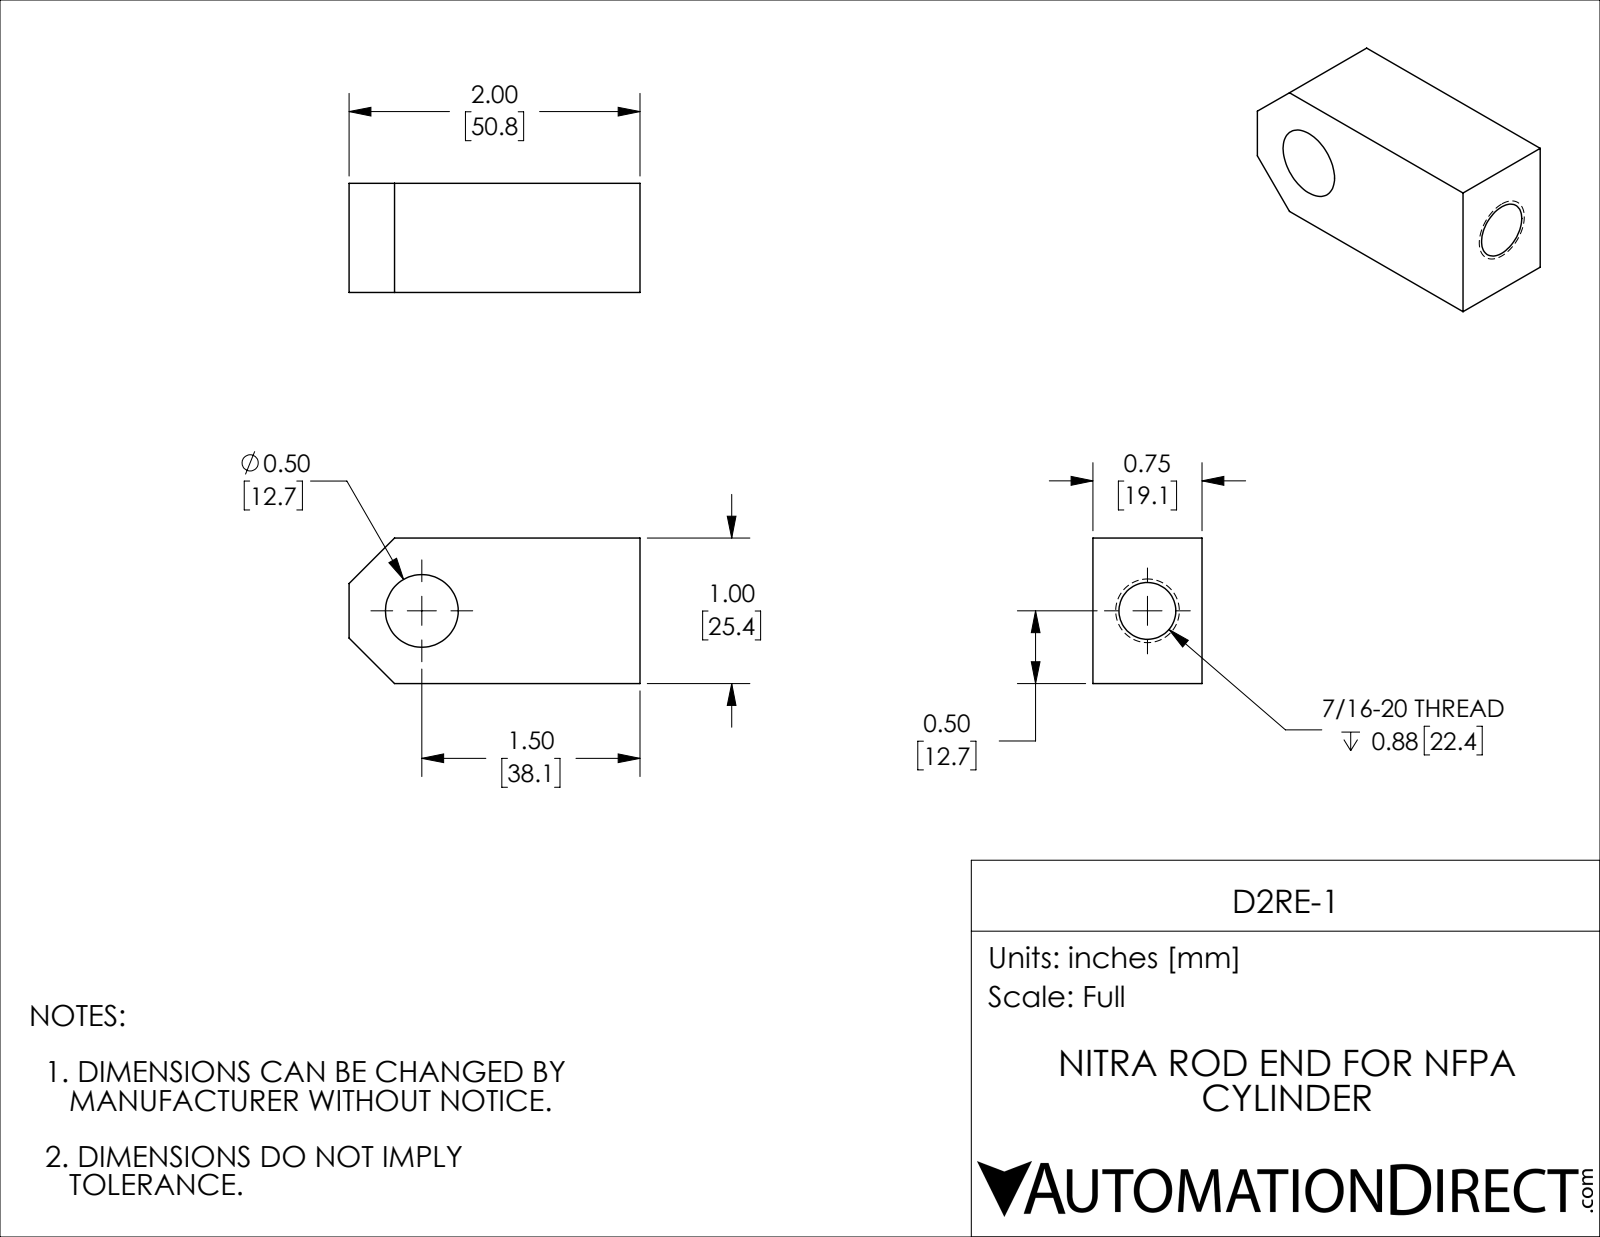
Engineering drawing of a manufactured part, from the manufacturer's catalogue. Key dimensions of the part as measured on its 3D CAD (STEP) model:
Part name (STEP PRODUCT): D2RE-1
STEP written by: SolidWorks 2019 (CONFIG_CONTROL_DESIGN)
Units: inches
Bodies: 1 solid, 14 faces (8 planar, 4 cylindrical, 2 other)
Overall size (bounding box): 2 × 1 × 0.75
Volume: 1.155 in³ · Surface area: 10.06 in²
Round holes (diameter × count): ⌀0.391 ×1, ⌀0.5 ×1
Main face-to-face distances: 0.75, 1, 2
